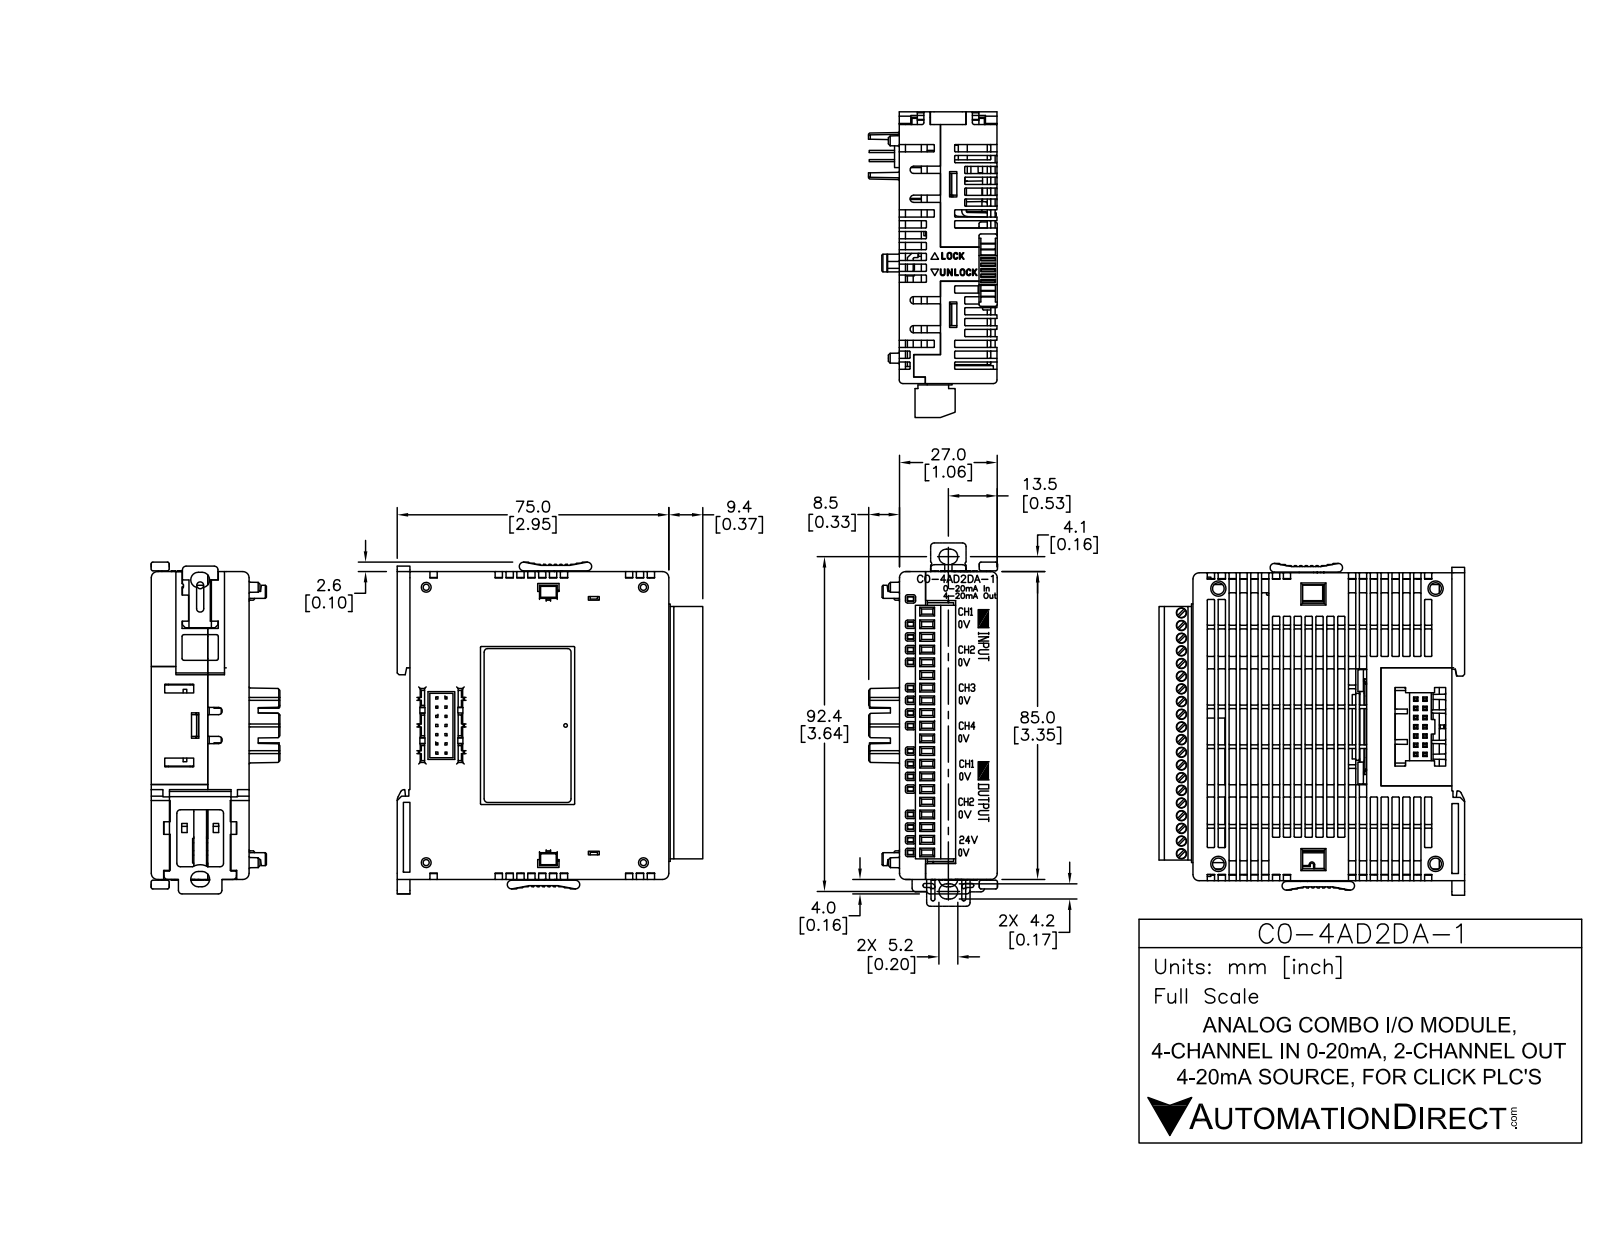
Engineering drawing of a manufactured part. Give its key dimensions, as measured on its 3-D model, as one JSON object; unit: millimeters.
{"part_name": "C0-4AD2DA-1", "step_written_by": "SolidWorks 2013 (AUTOMOTIVE_DESIGN)", "units": "millimeters", "bodies": {"solids": 1, "faces": 4124, "planar": 2924, "cylindrical": 1037, "other": 163}, "overall_size": [91.6, 84.4, 35.55], "volume_mm3": 165092, "surface_area_mm2": 33637, "round_holes": [[1, 20], [2.8, 20], [3.2, 4], [2, 2]], "round_bosses_or_shafts": [[2.6, 20], [1.9, 1]], "partial_cylinders_radius": [[0.2, 570], [0.5, 43], [0.3, 22], [2.8, 20], [1, 18], [1.2, 12], [1.7, 6], [2.1, 4]], "face_to_face_distances": [0.5, 27.01, 0.51, 26.5, 71.5, 85, 1.7, 26.3, 26.81, 3.5], "hole_center_spacings": [3.5, 7, 10.5, 14, 17.5, 21, 24.5, 28]}
